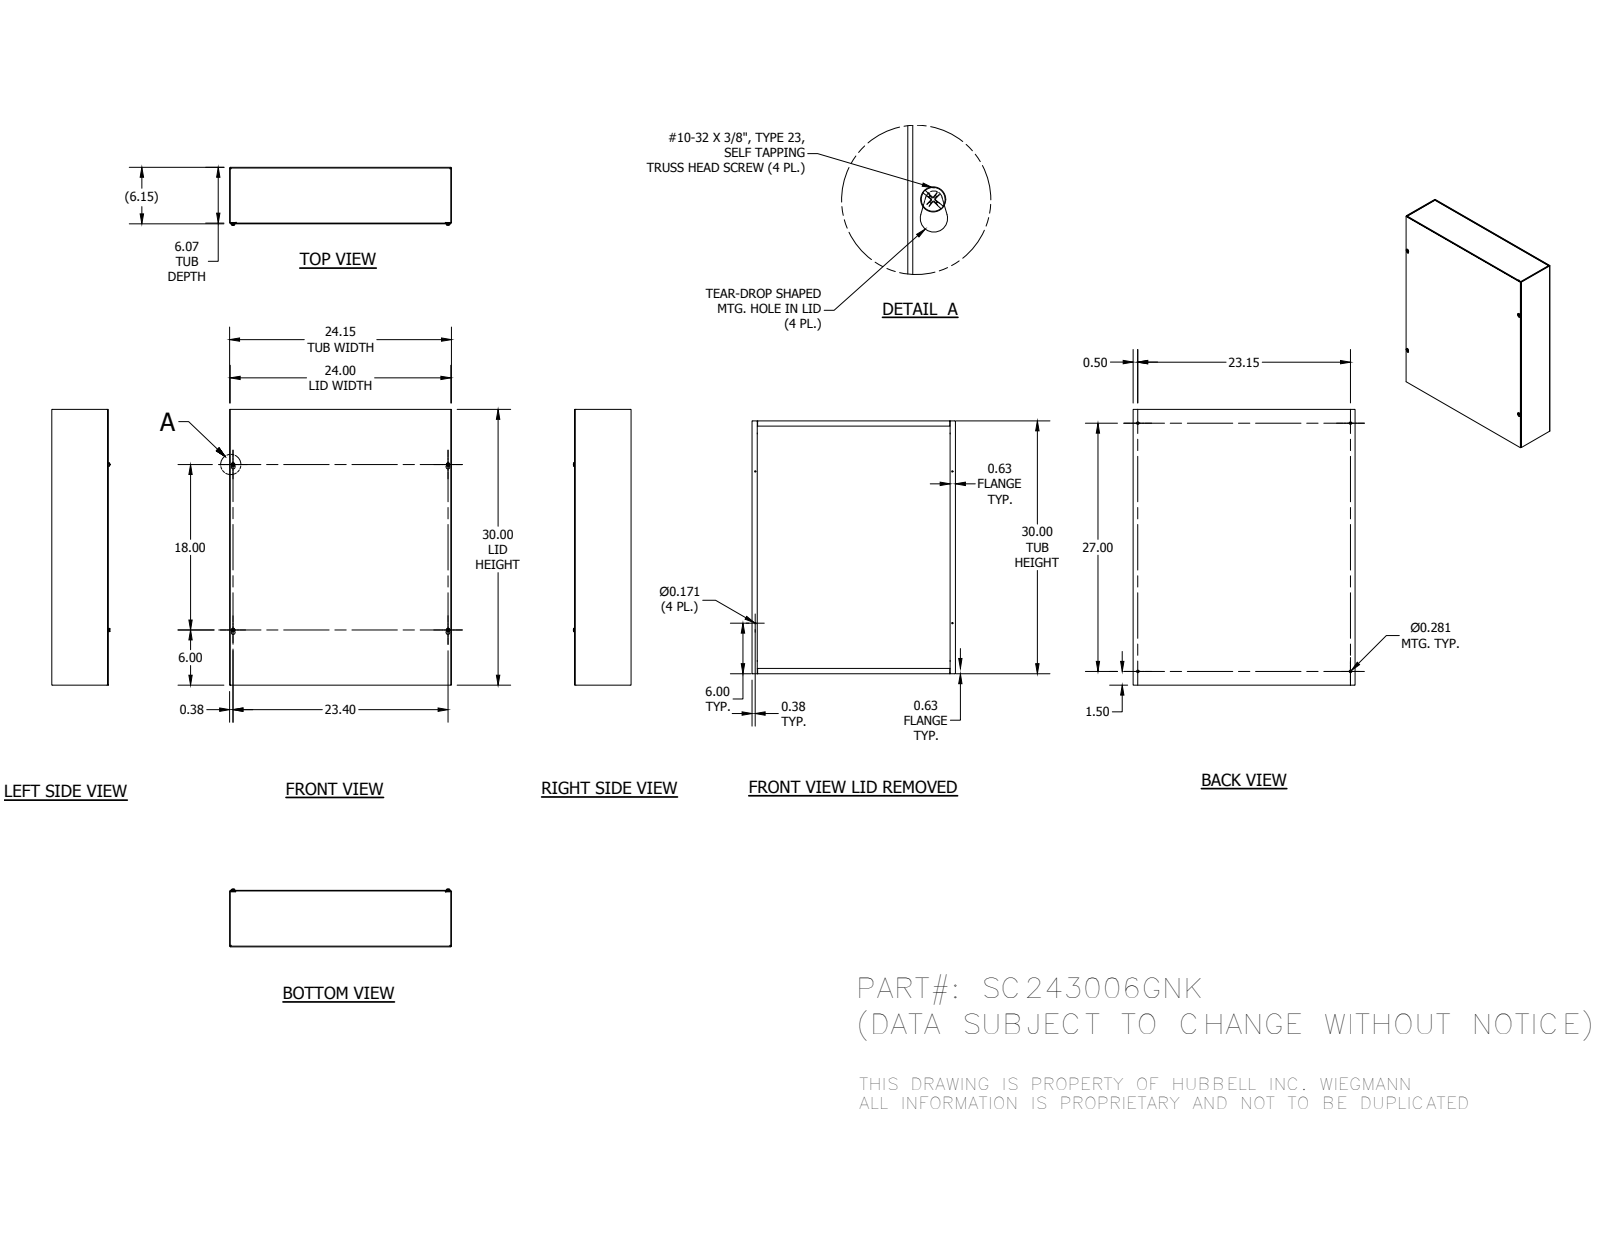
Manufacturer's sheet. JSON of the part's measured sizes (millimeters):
{"part_name": "SC243006GNKBLR; SC2406GNKTB; SC2430GLPA; 37214 (+1 more)", "step_written_by": "Autodesk Inventor 2014 (AUTOMOTIVE_DESIGN)", "units": "millimeters", "bodies": {"solids": 8, "faces": 320, "planar": 192, "cylindrical": 44, "other": 84}, "overall_size": [762, 613.36, 159.51], "volume_mm3": 2649000, "surface_area_mm2": 2837000, "round_holes": [[4.34, 4], [7.14, 4]], "round_bosses_or_shafts": [[4.83, 4]], "partial_cylinders_radius": [[0.4, 12], [2.28, 12], [3.17, 4], [5.16, 4]], "face_to_face_distances": [1.88, 154.28, 152.4, 156.16, 611.48, 760.12, 609.6, 613.36, 762, 758.24], "hole_center_spacings": [114.34, 571.51, 602.08, 822.22, 457.2, 587.96, 594.3, 685.8]}
